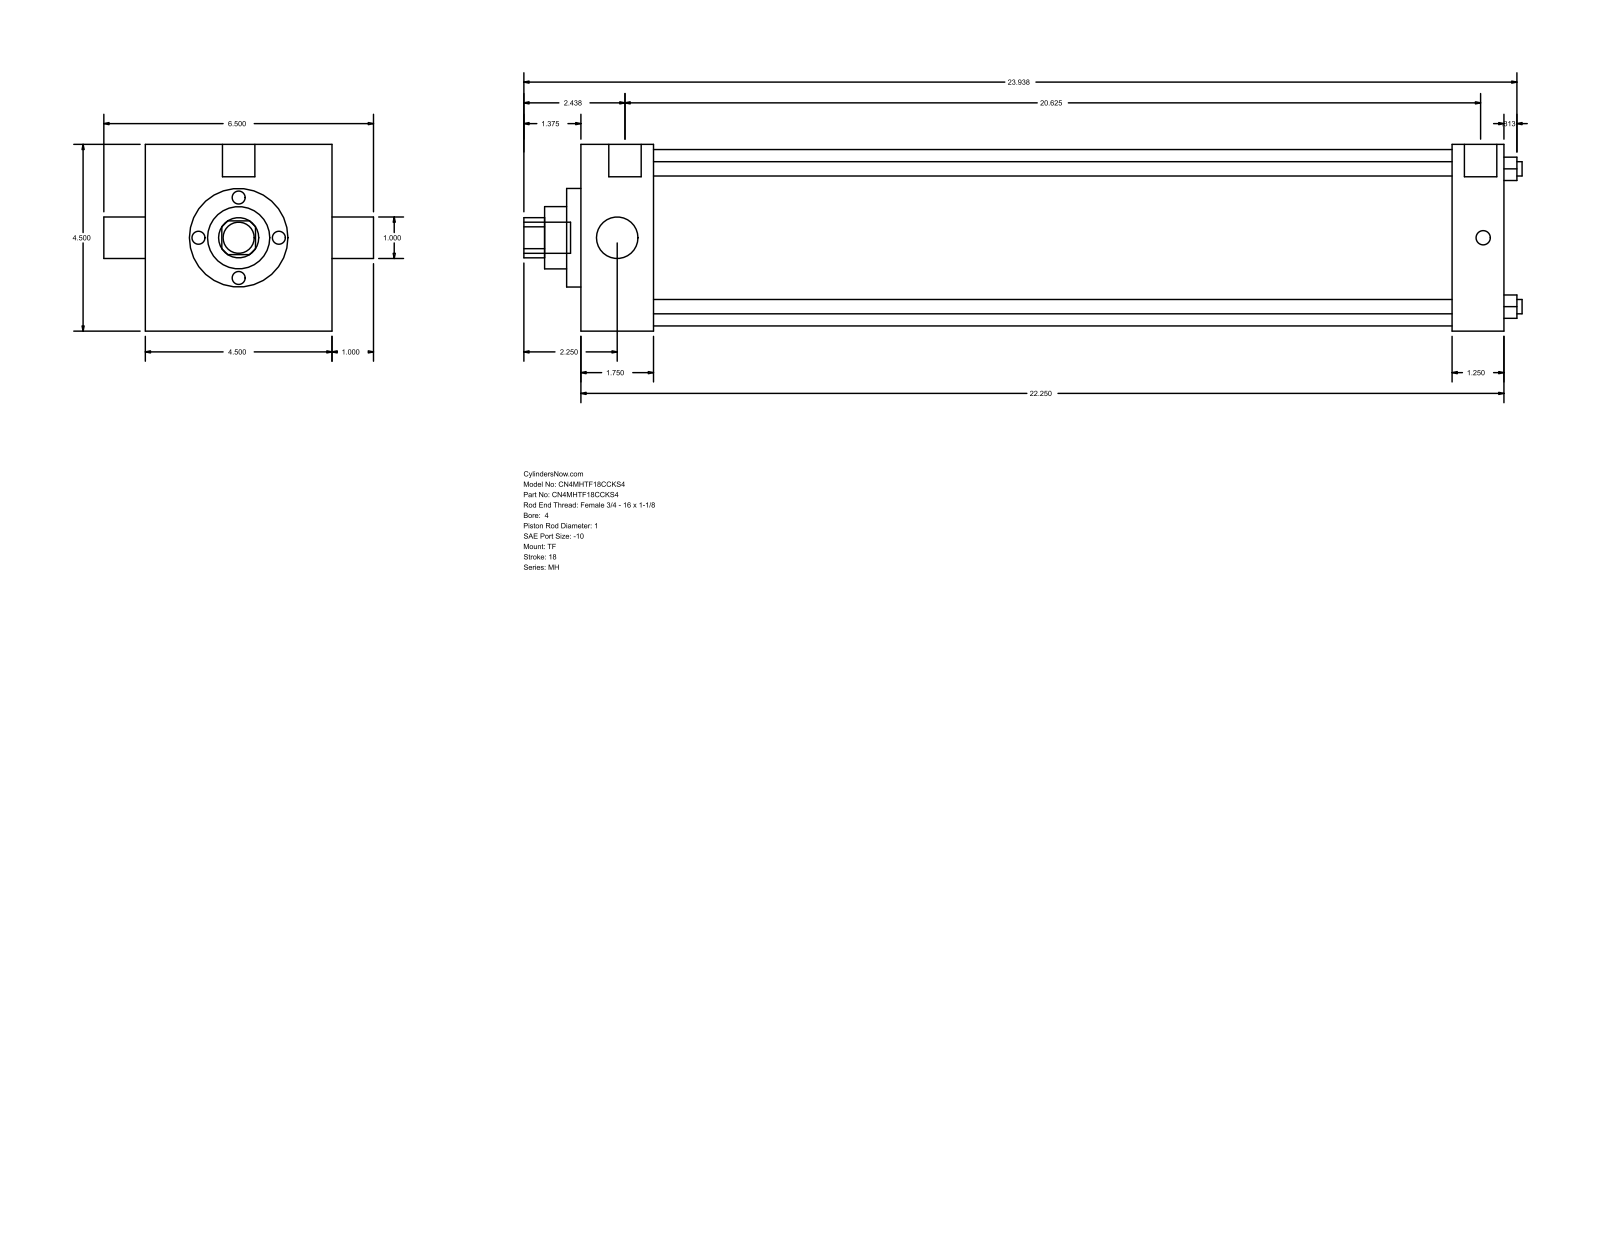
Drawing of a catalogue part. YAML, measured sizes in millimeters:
part_name: "MH_TF__0400_1"
step_written_by: "GSSL Pune (CONFIG_CONTROL_DESIGN)"
units: millimeters
bodies: {solids: 0, faces: 86, planar: 61, cylindrical: 25, other: 0}
overall_size: [611.19, 165.1, 114.3]
round_holes:
  - {diameter: 8.76, count: 4}
  - {diameter: 25.4, count: 2}
  - {diameter: 38.1, count: 1}
  - {diameter: 60.33, count: 1}
  - {diameter: 107.95, count: 1}
round_bosses_or_shafts:
  - {diameter: 8.73, count: 3}
  - {diameter: 19.84, count: 2}
  - {diameter: 19.05, count: 1}
partial_cylinders:
  - {radius: 12.29, count: 1}
face_to_face_distances: [114.3, 565.16, 44.46, 520.7, 533.41, 488.95, 31.75, 8.73, 53.19, 542.14]
hole_center_spacings: [59.62, 84.32, 119.25]
